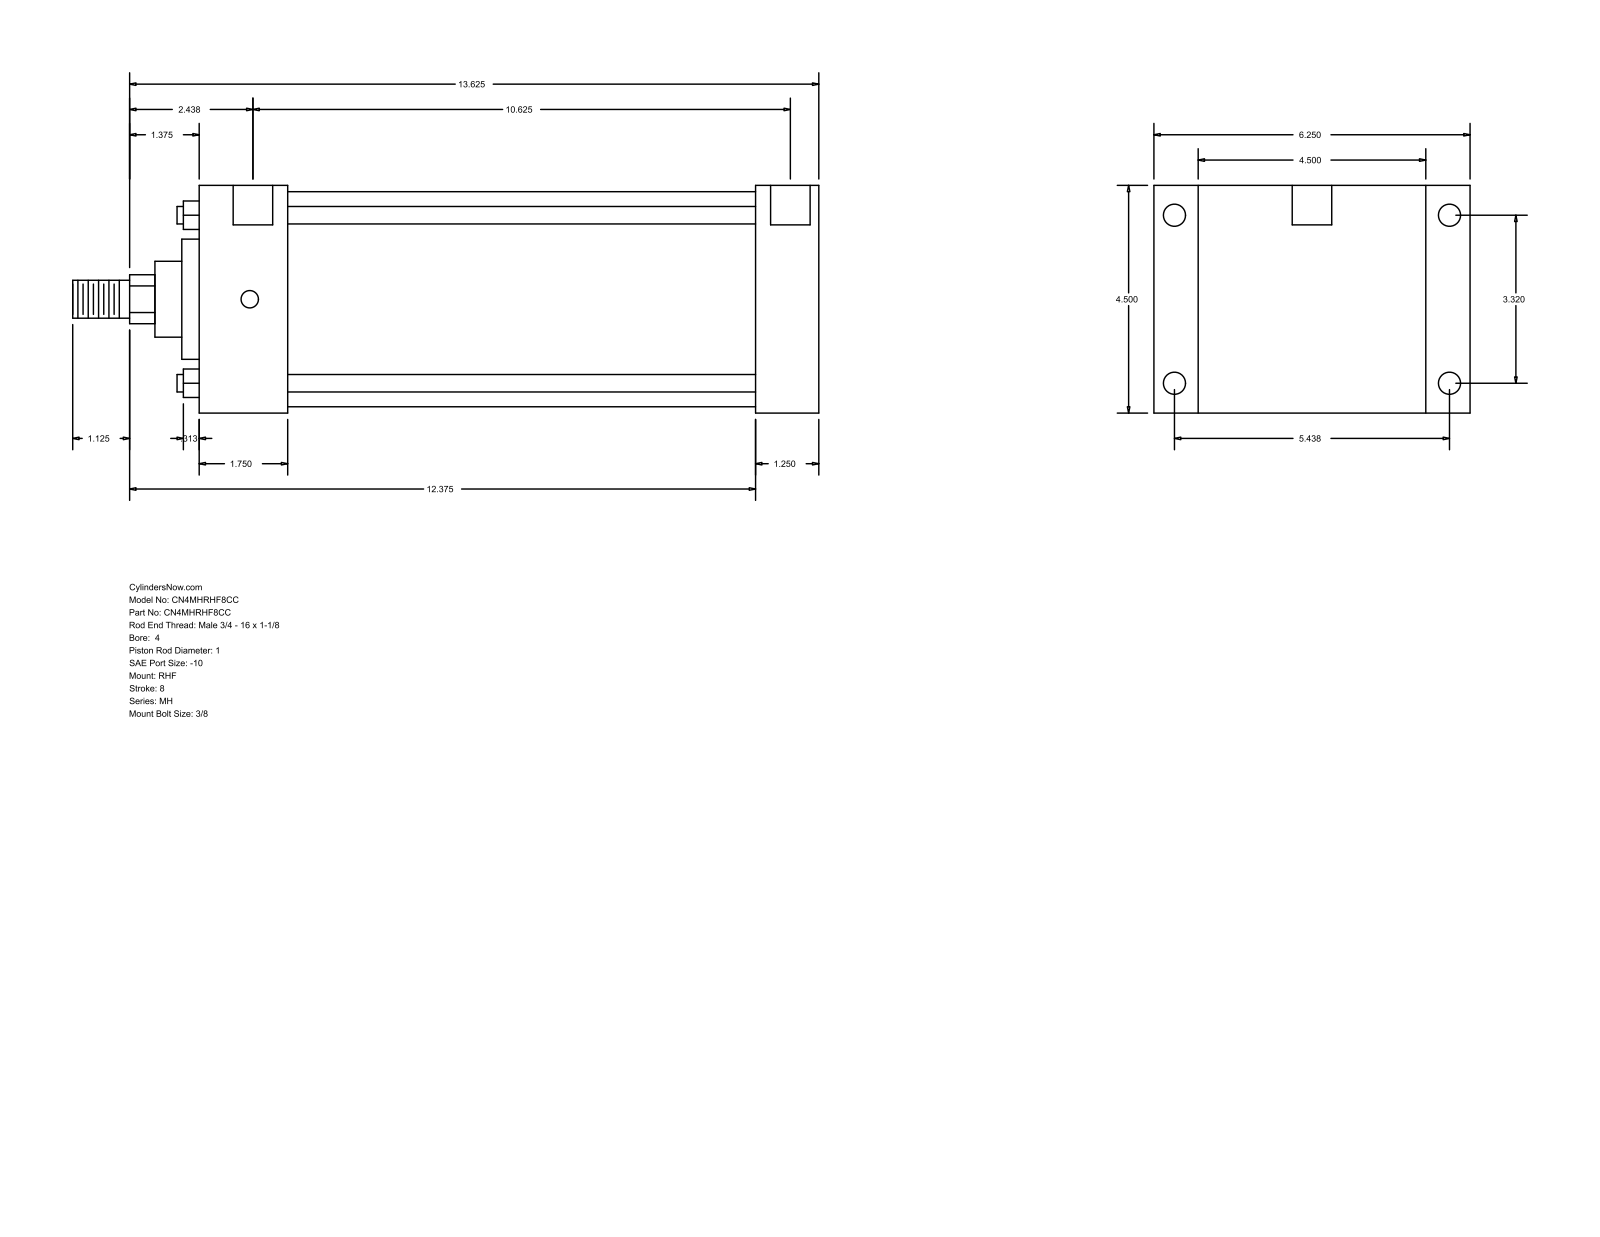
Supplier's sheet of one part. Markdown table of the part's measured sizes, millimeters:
| quantity | value |
| --- | --- |
| part name | MH_RHF__0400_1 |
| STEP written by | GSSL Pune (CONFIG_CONTROL_DESIGN) |
| units | millimeters |
| bodies | 0 solids, 90 faces (61 planar, 29 cylindrical, 0 other) |
| overall size | 374.65 × 158.75 × 114.3 |
| round holes (diameter × count) | 8.73 × 4, 11.13 × 4, 19.84 × 2 |
| round bosses / shafts (diameter × count) | 8.76 × 4, 107.95 × 1, 60.33 × 1, 38.1 × 1, 25.4 × 1, 19.05 × 1 |
| partial cylindrical surfaces (radius × count) | 12.29 × 1 |
| main face-to-face distances | 114.3, 311.15, 279.4, 31.75, 22.23, 136.53, 44.46, 234.94, 266.69, 158.76 |
| hole center spacings | 84.32, 138.12, 161.82, 273.05, 1.58, 1.59, 269.88, 271.46 |
